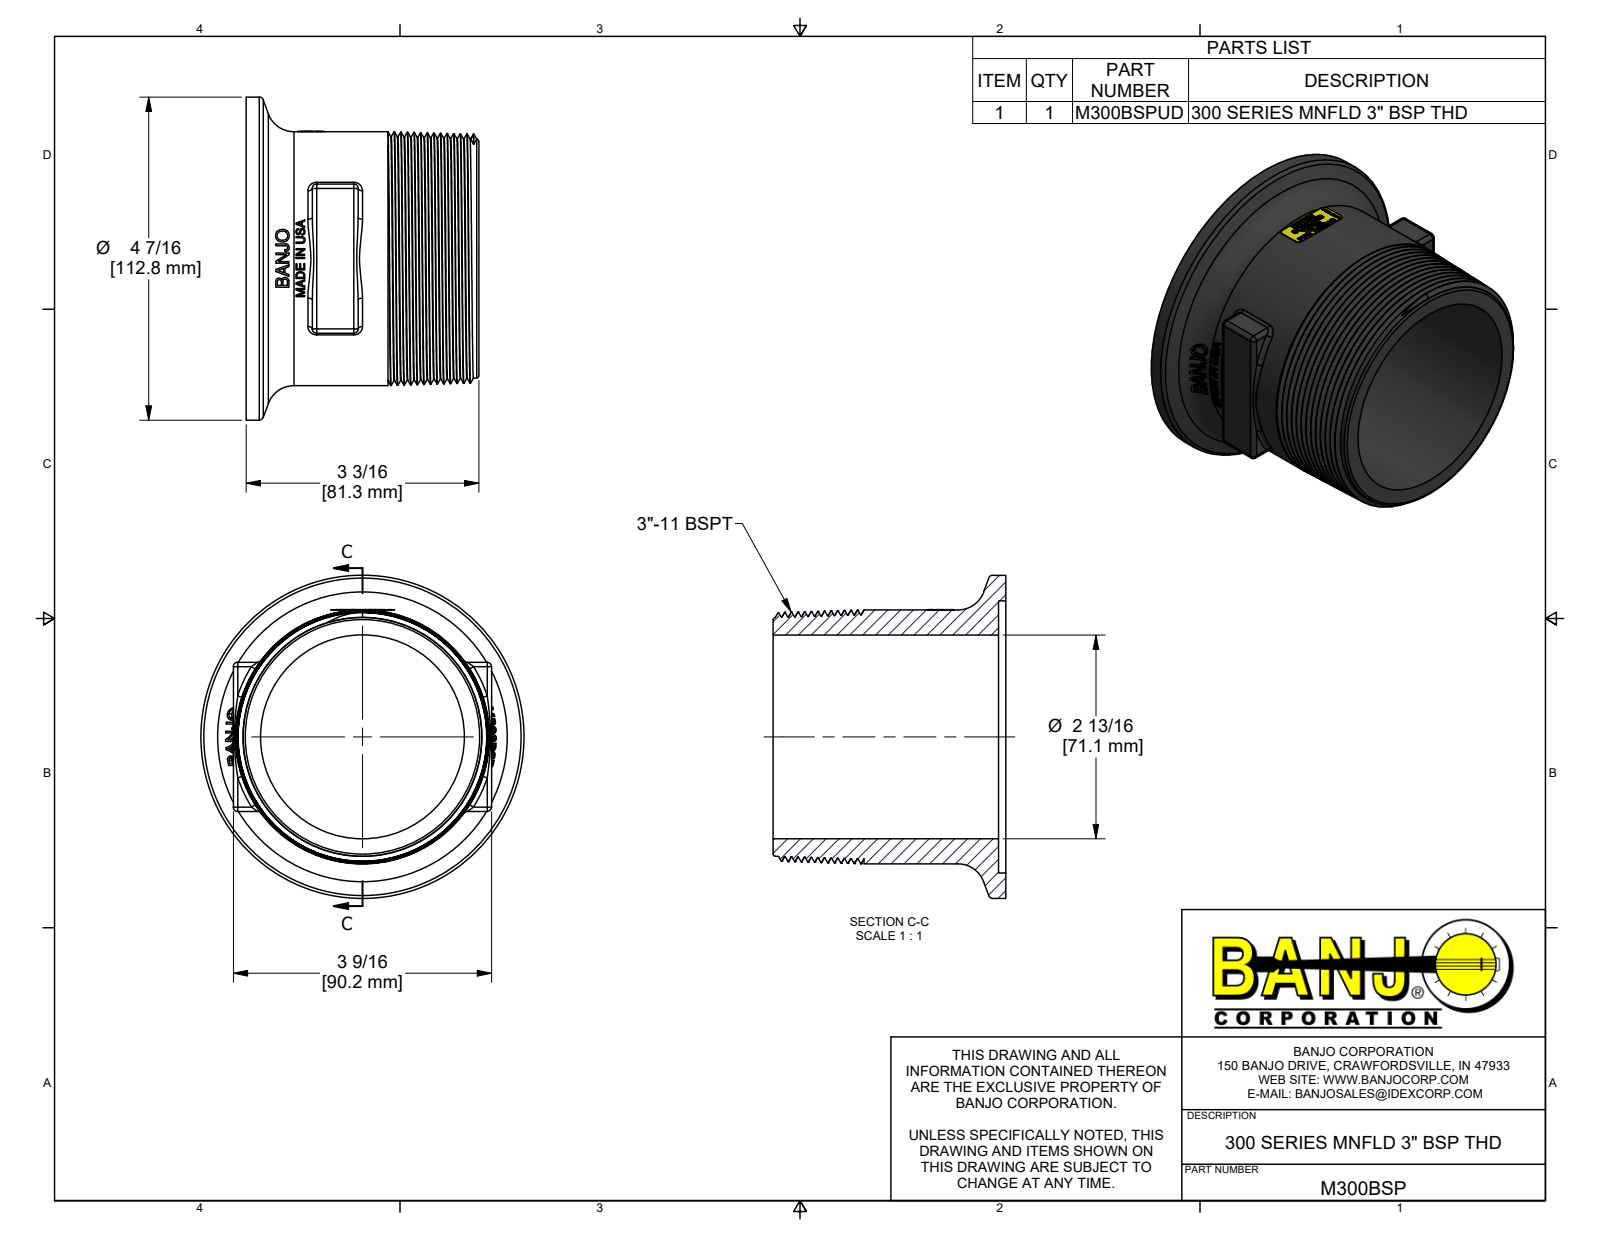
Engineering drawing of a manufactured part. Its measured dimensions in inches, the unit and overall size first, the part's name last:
Units: inches
Overall size (bounding box): 4.44 × 4.44 × 3.2
Round holes (diameter × count): ⌀2.8 ×1, ⌀3.74 ×1
Round bosses / shafts (diameter × count): ⌀4.44 ×1, ⌀3.49 ×1
Partial cylindrical surfaces — rounded edges, fillets, slot ends (radius × count): R0.06 ×16, R0.888 ×1, R1.775 ×1
Main face-to-face distances: 0.1, 3.2, 3.1, 3.55, 1.25, 1.95, 1.85, 2.05, 1.54, 1.44
Volume: 11.98 in³ · Surface area: 91.64 in²
Bodies: 1 solid, 423 faces (175 planar, 37 cylindrical, 211 other)
Part name (STEP PRODUCT): M300BSP
STEP written by: Autodesk Inventor 2018 (AUTOMOTIVE_DESIGN)
